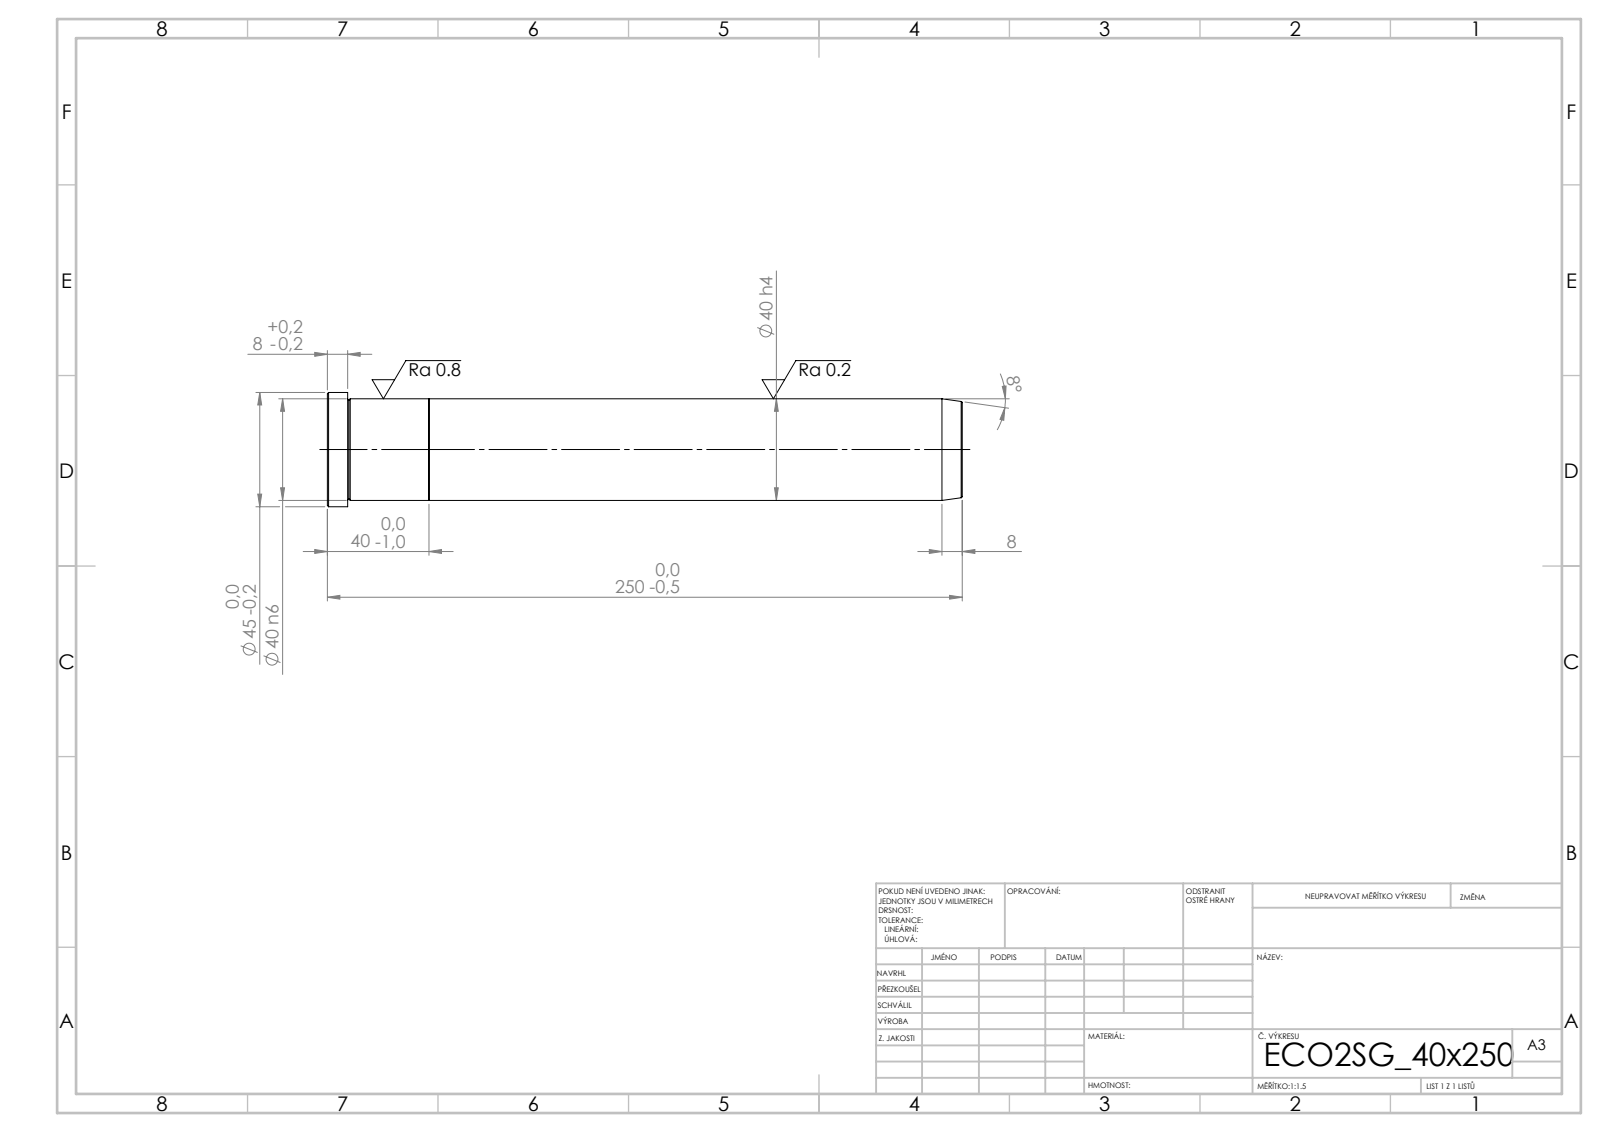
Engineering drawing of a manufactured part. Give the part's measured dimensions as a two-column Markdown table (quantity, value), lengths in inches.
| quantity | value |
| --- | --- |
| STEP written by | SolidWorks 2019 (CONFIG_CONTROL_DESIGN) |
| units | inches |
| bodies | 2 solids, 21 faces (5 planar, 6 cylindrical, 10 other) |
| overall size | 9.843 × 1.772 × 1.772 |
| volume | 19.3 in³ |
| surface area | 57.49 in² |
| round bosses / shafts (diameter × count) | 1.772 × 1, 1.575 × 1 |
| main face-to-face distances | 1.575, 8.268, 9.843, 9.528, 1.26, 0.315 |
